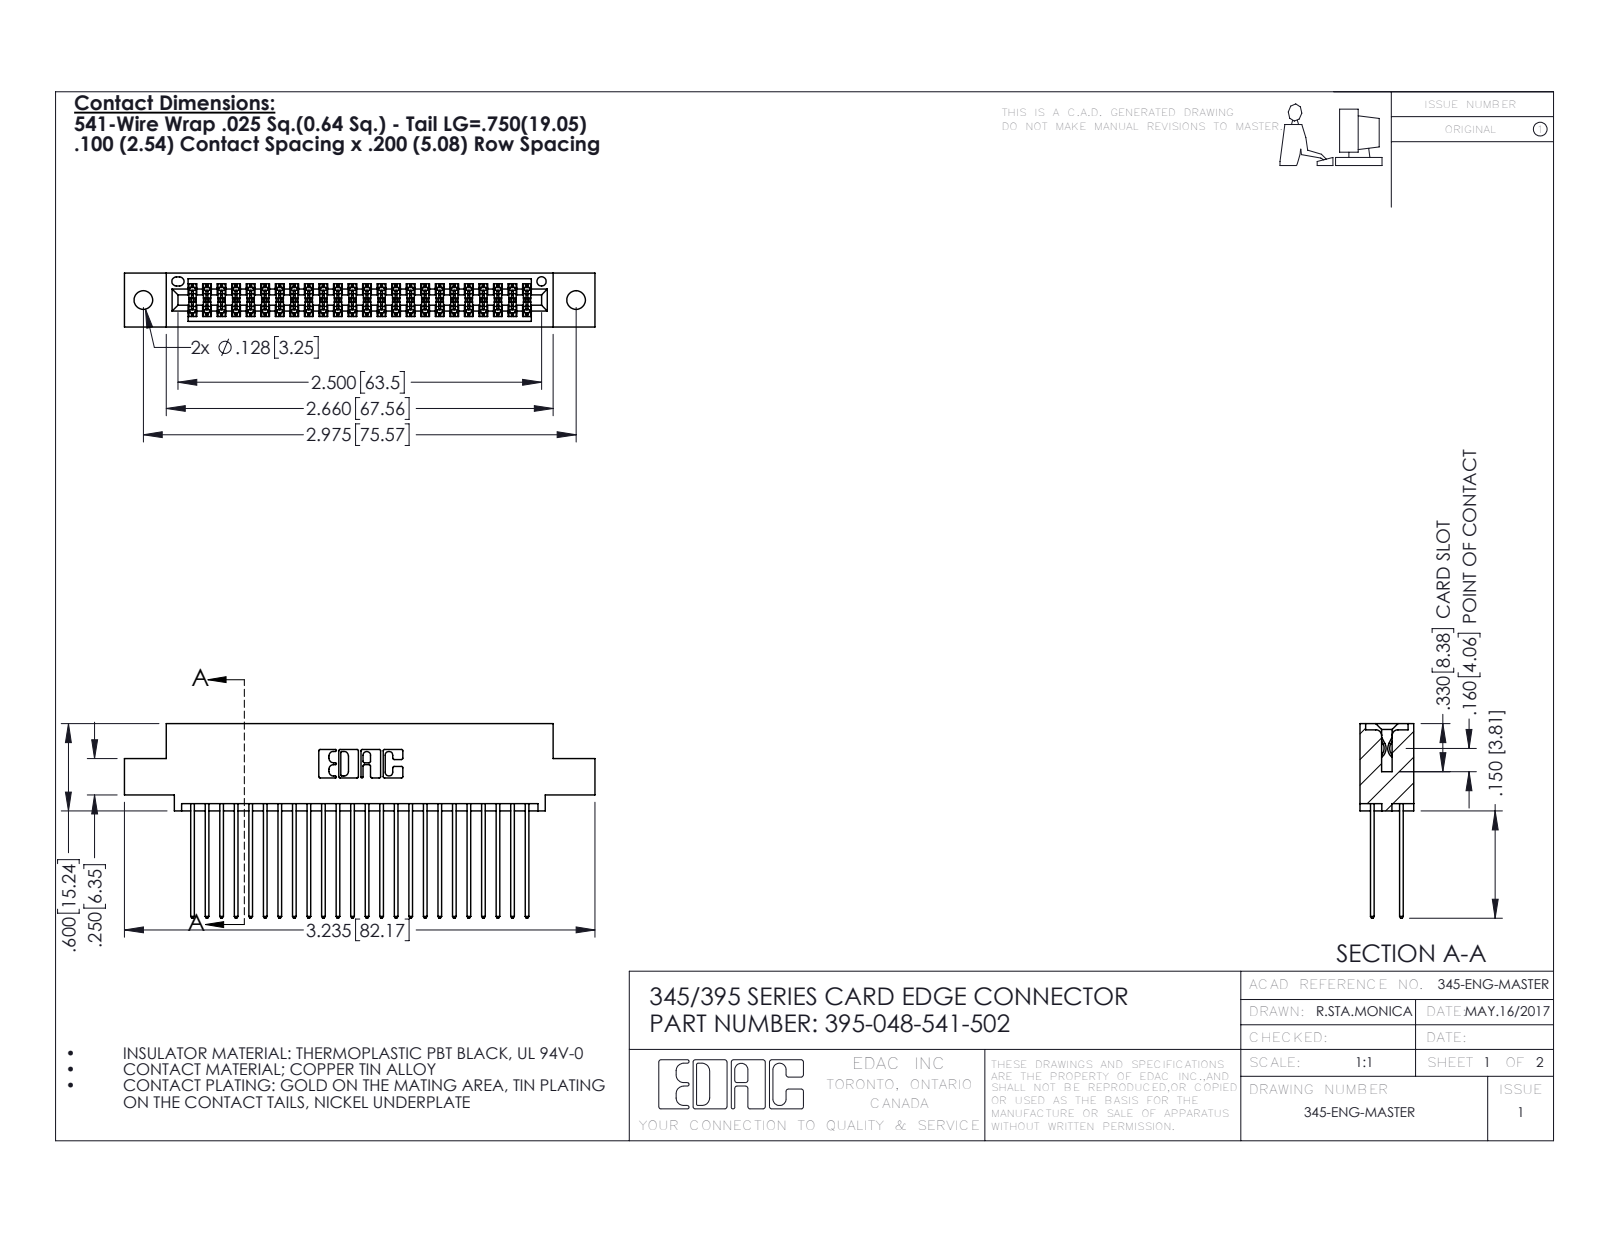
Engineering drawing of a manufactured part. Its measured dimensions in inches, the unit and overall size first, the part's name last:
Units: inches
Overall size (bounding box): 3.235 × 1.337 × 0.37
Round holes (diameter × count): ⌀0.128 ×2, ⌀0.064 ×1
Partial cylindrical surfaces — rounded edges, fillets, slot ends (radius × count): R0.006 ×72, R0.01 ×48, R0.01 ×22, R0.007 ×6, R0.031 ×6, R0.026 ×3, R0.014 ×2, R0.019 ×2
Main face-to-face distances: 0.298, 0.072, 0.2, 0.098, 0.272, 0.025, 0.37, 0.225, 0.175, 0.149
Hole centre spacings: 0.27, 2.741, 2.975
Volume: 0.487 in³ · Surface area: 19.47 in²
Bodies: 49 solids, 2530 faces (1668 planar, 862 cylindrical, 0 other)
Part name (STEP PRODUCT): 345-292-001_345-293-141; 395-048-541-502; 345 Part_0.110 Offset - 0.128 Dia
STEP written by: SolidWorks 2016 (CONFIG_CONTROL_DESIGN)
